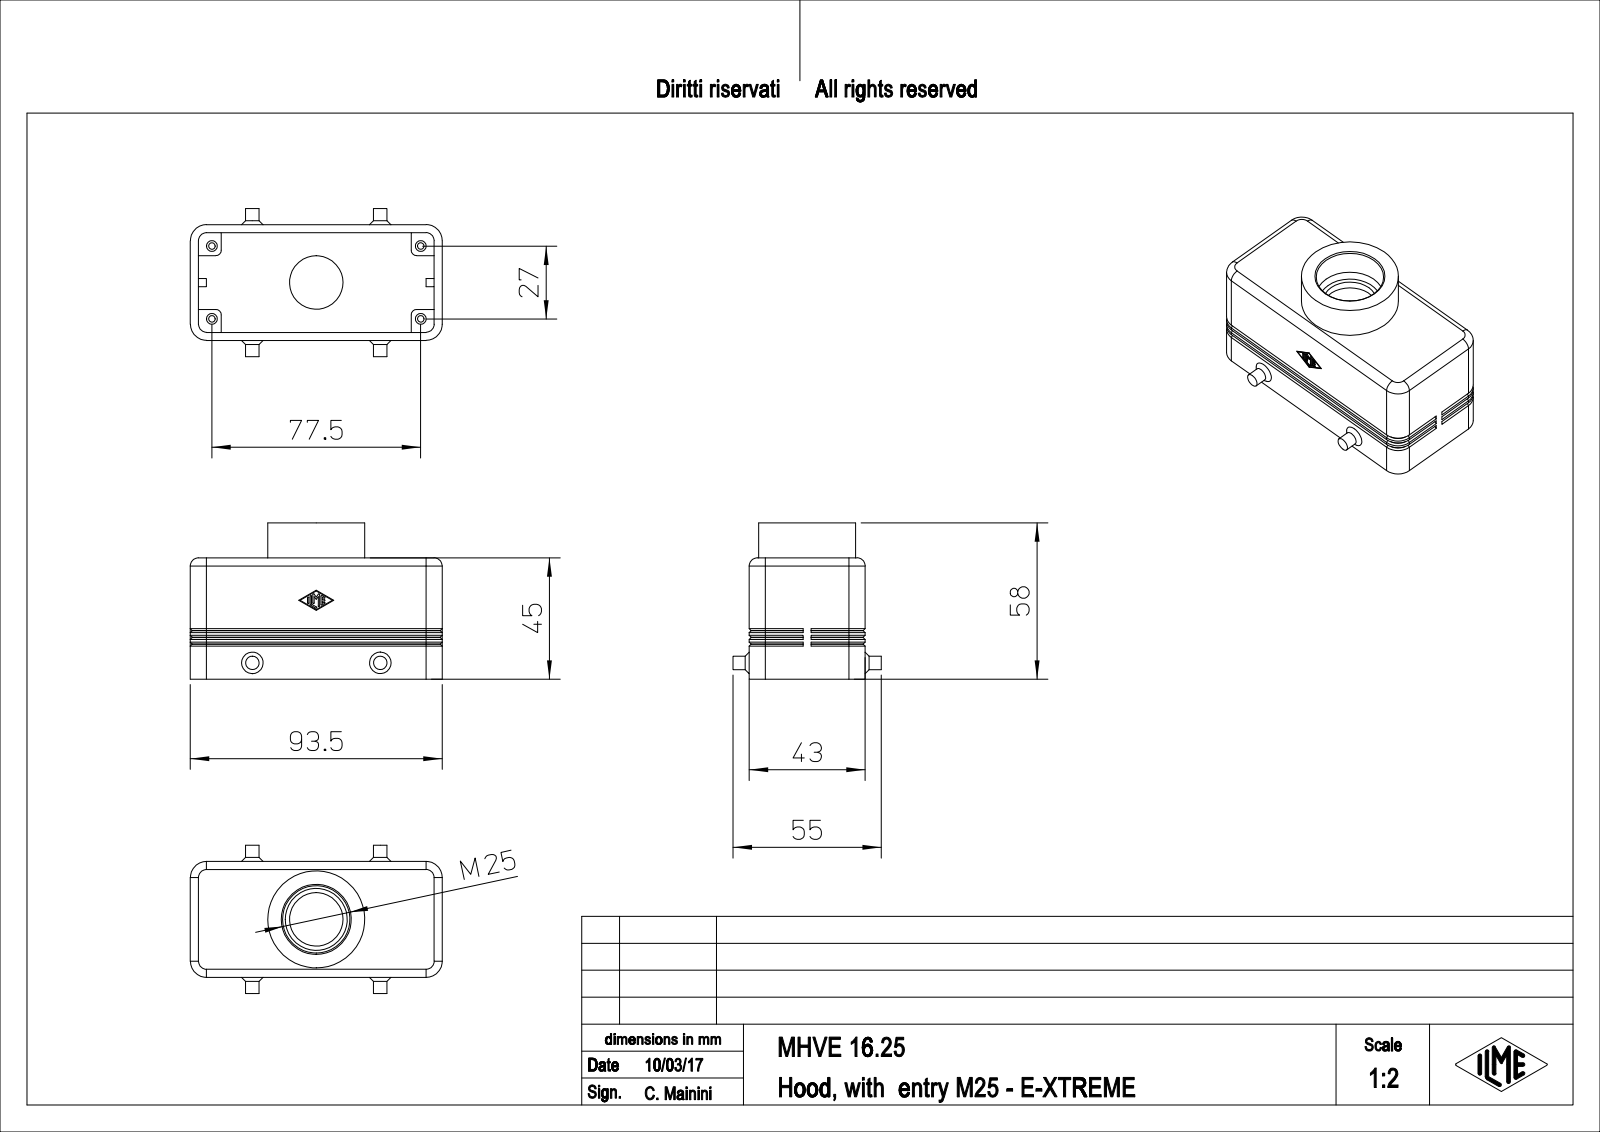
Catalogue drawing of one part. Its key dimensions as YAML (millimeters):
part_name: "MHVE_16.25"
step_written_by: "PTC Creo Elements/Direct Modeling 19.0E 27-Jun-2016 (C) Parametric Technology GmbH (AUTOMOTIVE_DESIGN)"
units: millimeters
bodies: {solids: 1, faces: 282, planar: 148, cylindrical: 86, other: 48}
overall_size: [93.5, 58, 55]
volume: 58904
surface_area: 33271
round_holes:
  - {diameter: 2.46, count: 4}
  - {diameter: 4, count: 4}
  - {diameter: 19.84, count: 1}
  - {diameter: 25, count: 1}
round_bosses_or_shafts:
  - {diameter: 5, count: 2}
  - {diameter: 36, count: 1}
partial_cylinders:
  - {radius: 0.25, count: 14}
  - {radius: 3, count: 8}
  - {radius: 2, count: 4}
  - {radius: 5.3, count: 4}
  - {radius: 6, count: 4}
  - {radius: 1.5, count: 1}
face_to_face_distances: [3, 40, 37, 43, 11.5, 8.5, 90.5, 20, 93.5, 87.5]
hole_center_spacings: [41.03, 27, 77.5, 82.07]
